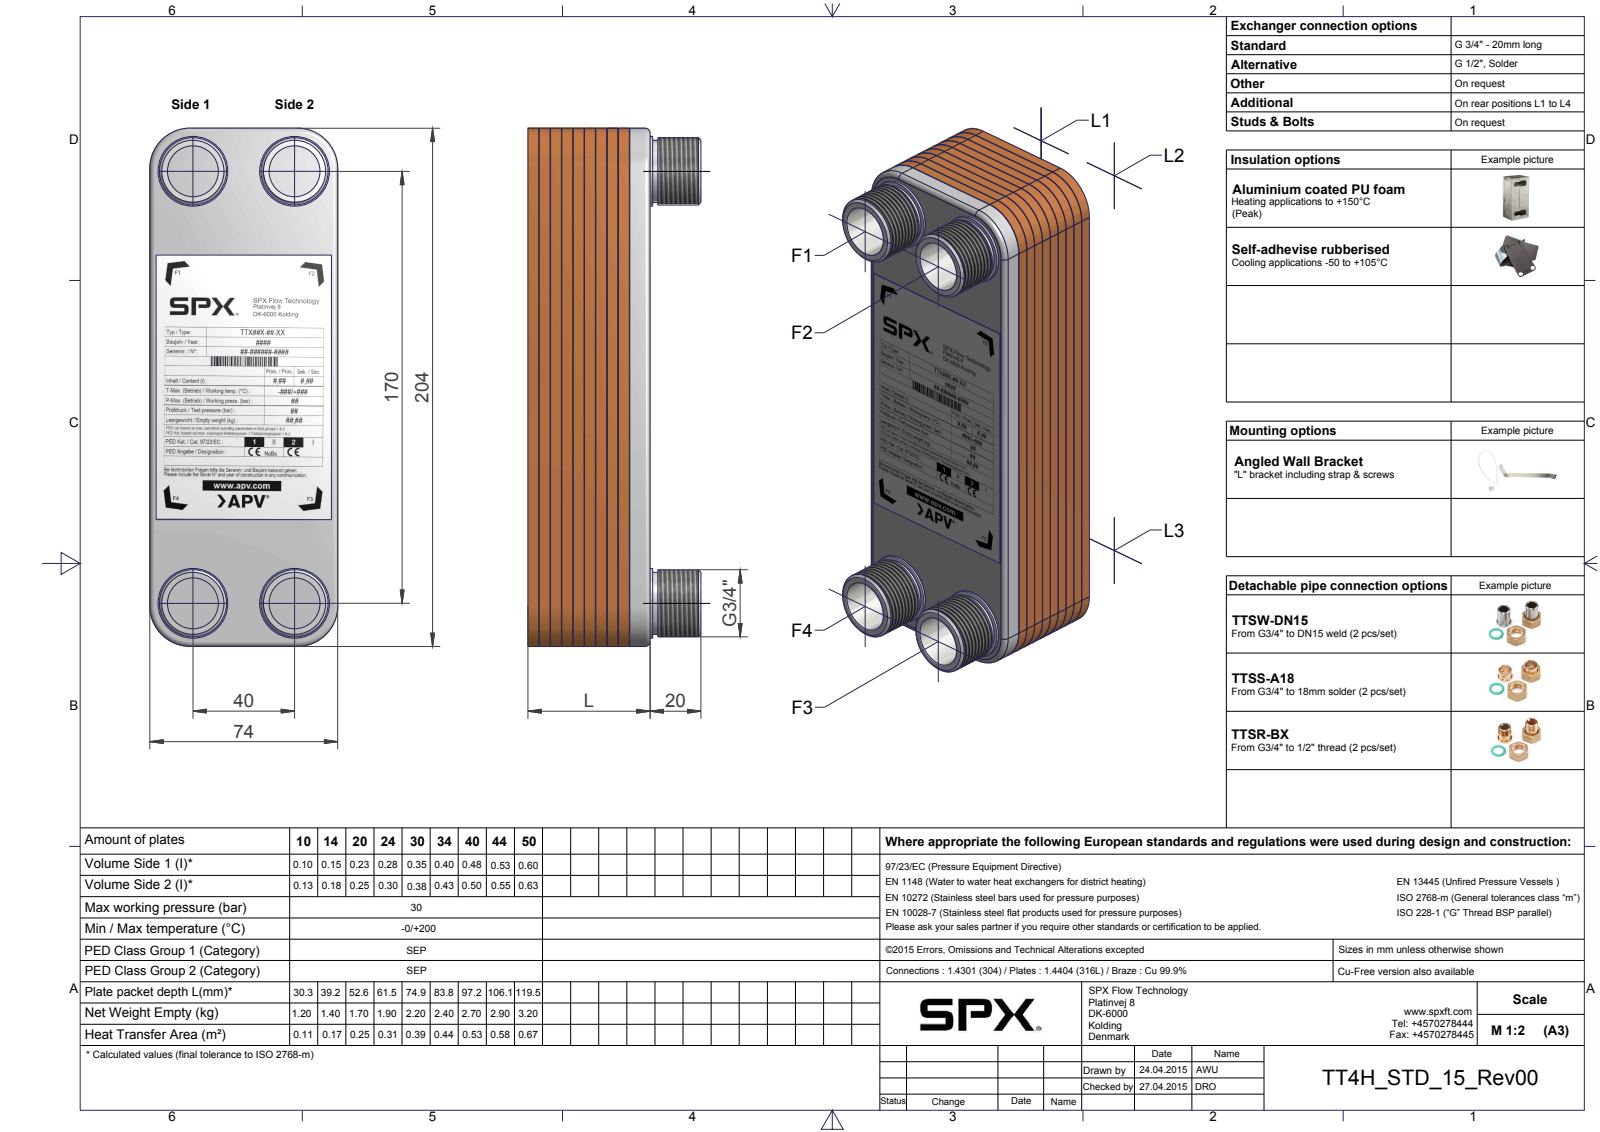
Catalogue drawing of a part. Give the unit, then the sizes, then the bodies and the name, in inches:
Units: inches
Overall size (bounding box): 8.031 × 3.937 × 2.913
Round holes (diameter × count): ⌀0.787 ×4
Round bosses / shafts (diameter × count): ⌀1.08 ×4, ⌀1.041 ×4, ⌀0.962 ×4
Partial cylindrical surfaces — rounded edges, fillets, slot ends (radius × count): R0.079 ×4, R0.63 ×4
Main face-to-face distances: 0.176, 0.351, 0.527, 0.702, 0.878, 1.054, 1.229, 1.405, 0.315, 0.491
Hole centre spacings: 1.575, 6.693, 6.876
Volume: 48.83 in³ · Surface area: 593.2 in²
Bodies: 16 solids, 248 faces (136 planar, 64 cylindrical, 48 other)
Part name (STEP PRODUCT): Grundplatte; Kupferplatten; Schraube G3-4; PB4_Typenschild_Unex (+1 more)
STEP written by: Autodesk Inventor 2015 (AUTOMOTIVE_DESIGN)
